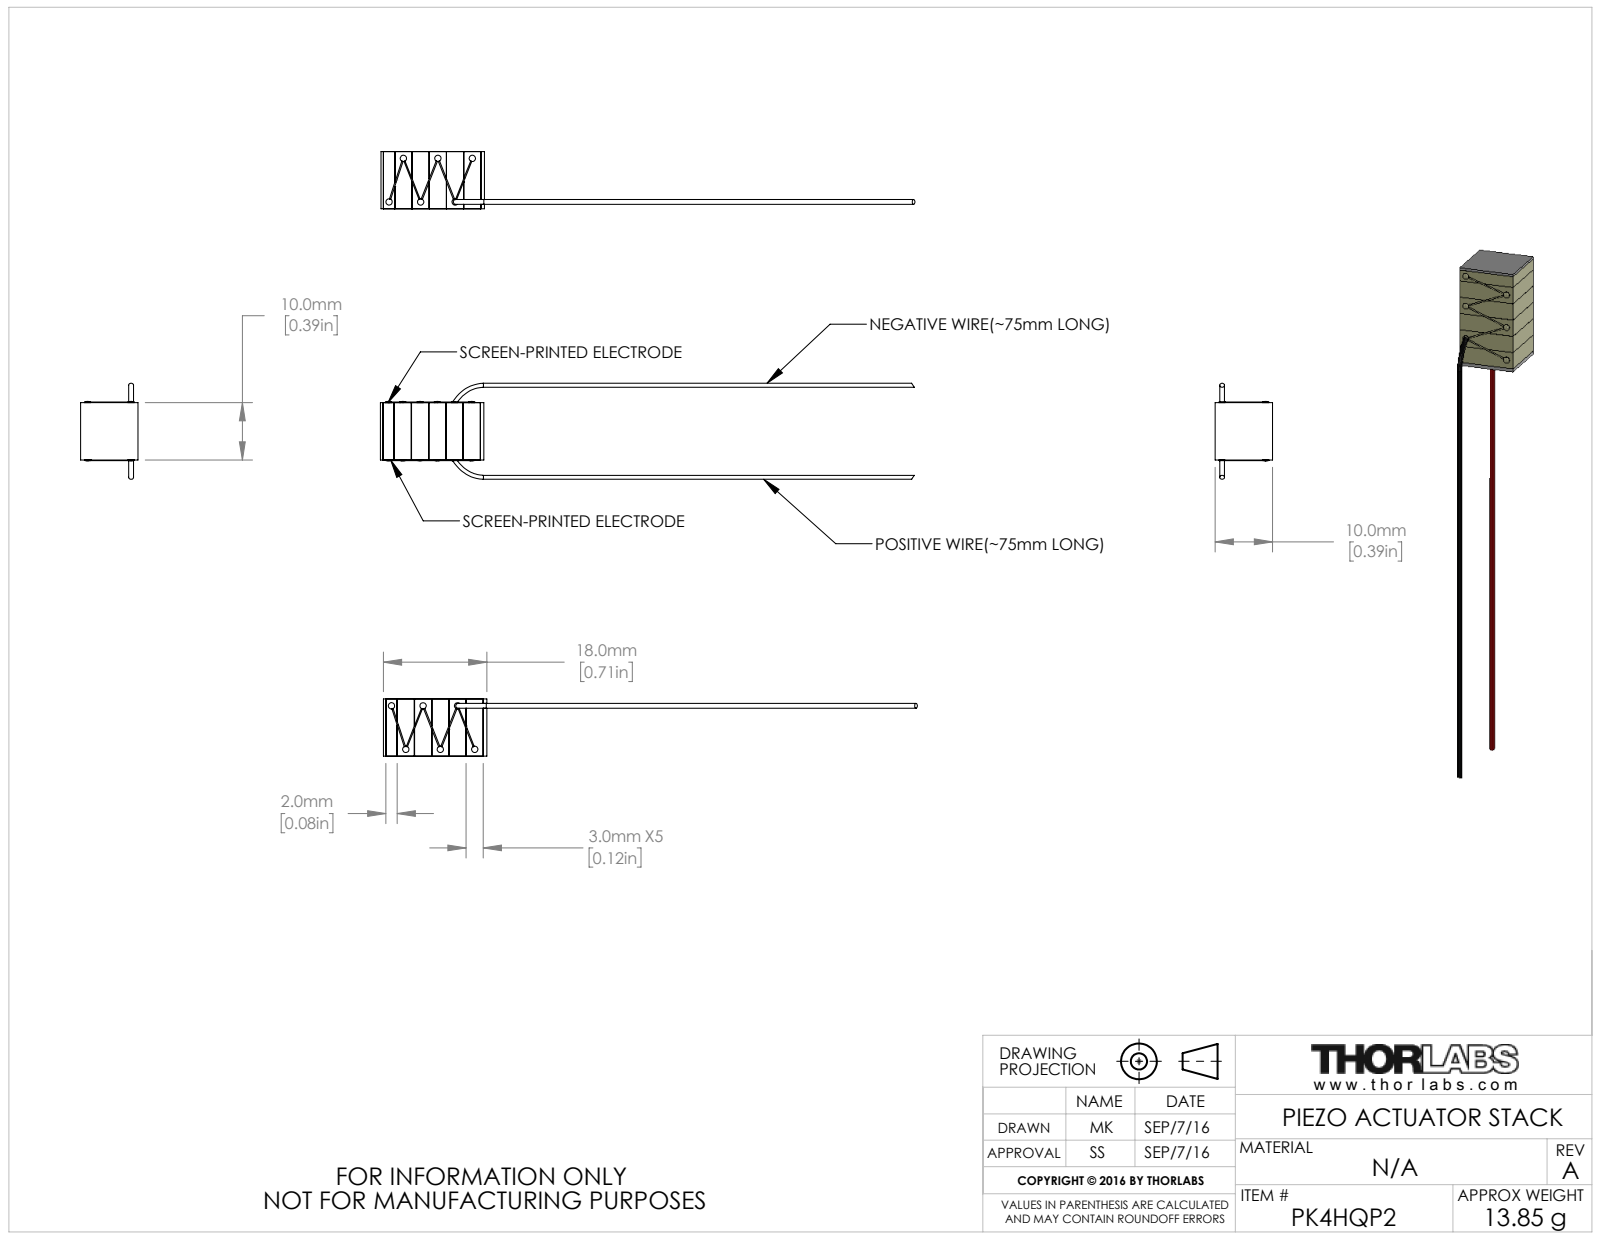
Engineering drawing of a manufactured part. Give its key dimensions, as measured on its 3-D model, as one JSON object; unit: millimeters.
{"part_name": "CTN003171", "step_written_by": "SolidWorks 2016 (AUTOMOTIVE_DESIGN)", "units": "millimeters", "bodies": {"solids": 4, "faces": 206, "planar": 118, "cylindrical": 36, "other": 52}, "overall_size": [93.22, 16.76, 10], "volume_mm3": 3578, "surface_area_mm2": 4623, "round_bosses_or_shafts": [[1.1, 6]], "face_to_face_distances": [3.01, 3, 6.01, 6.02, 10, 9.02, 12.03, 9.03, 3.02, 15.03]}
